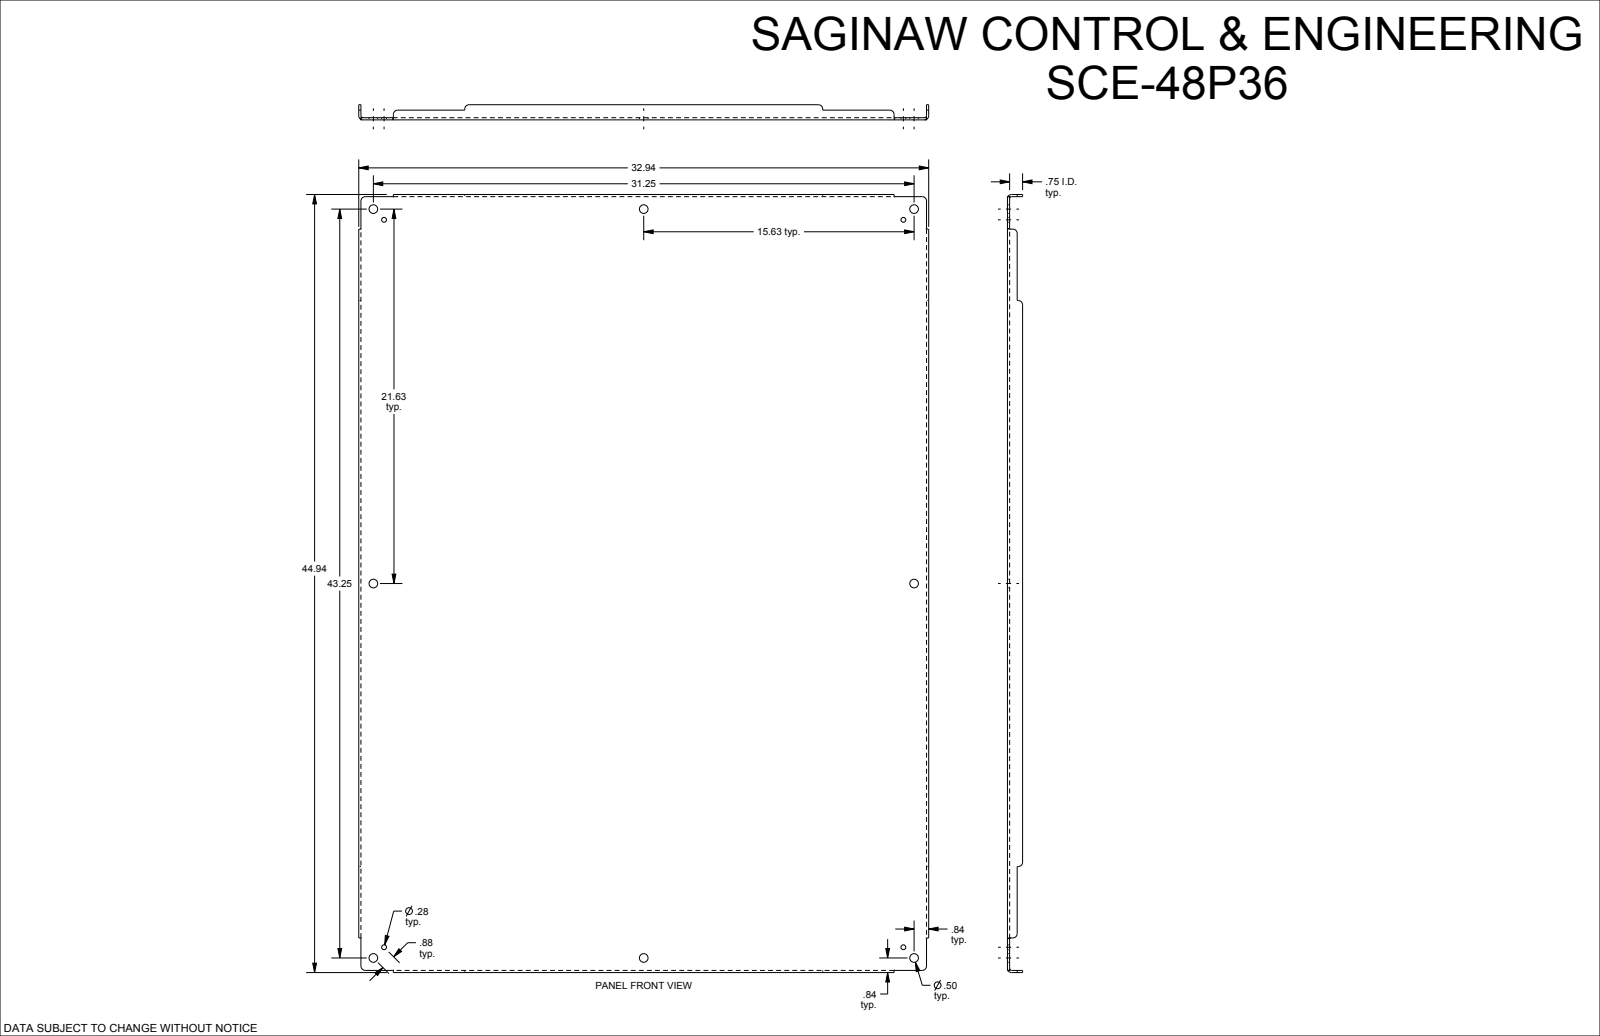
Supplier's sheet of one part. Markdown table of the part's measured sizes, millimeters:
| quantity | value |
| --- | --- |
| part name | SCE-48P36 |
| STEP written by | SolidWorks 2019 (CONFIG_CONTROL_DESIGN) |
| units | millimeters |
| bodies | 1 solid, 110 faces (46 planar, 40 cylindrical, 24 other) |
| overall size | 1141.4 × 836.6 × 22.2 |
| volume | 3 195 000 mm³ |
| surface area | 2 027 000 mm² |
| round holes (diameter × count) | 12.7 × 8, 7.1 × 4 |
| partial cylindrical surfaces (radius × count) | 6.4 × 12, 2.8 × 4, 6 × 4 |
| main face-to-face distances | 3.2, 3.2, 833.5, 1138.3, 830.2, 836.6, 1135, 1141.4, 19.1, 22.2 |
| hole center spacings | 22.2, 381.5, 396.9, 533.8, 549.3, 677.6, 778.2, 943.4 |
